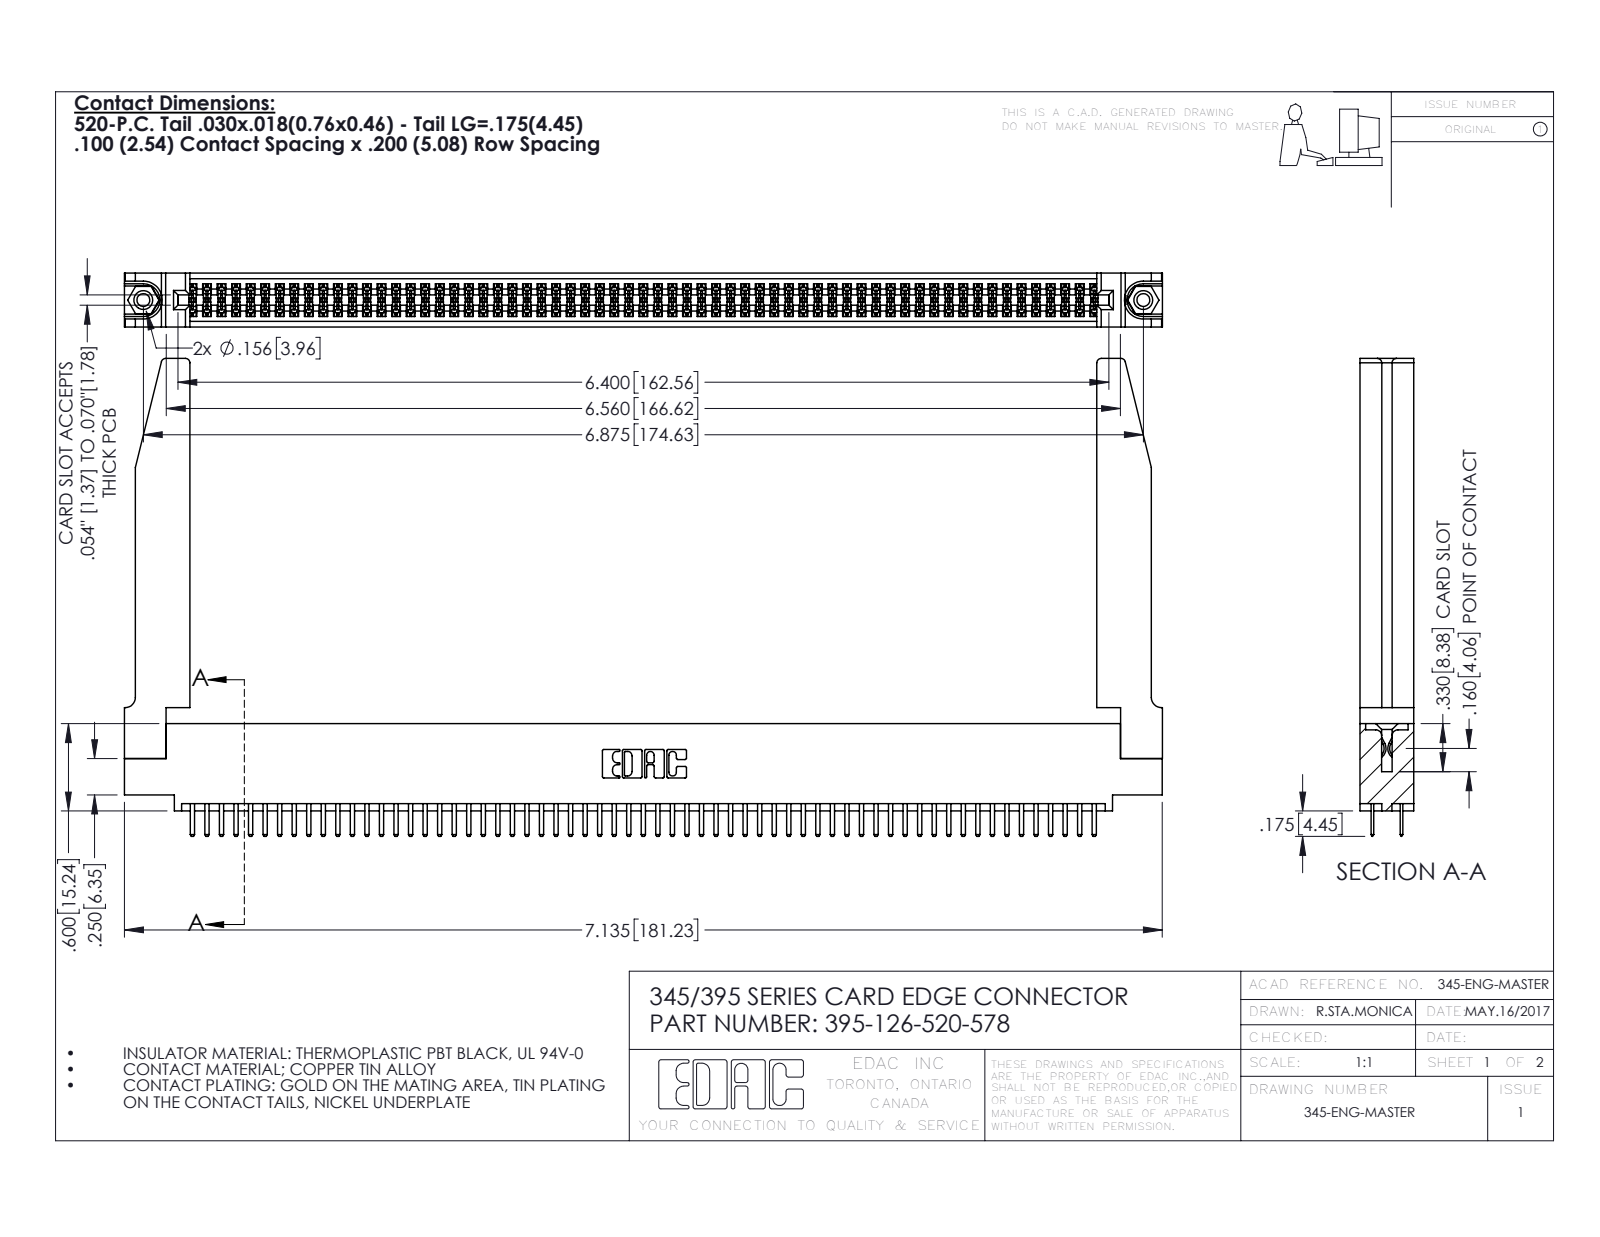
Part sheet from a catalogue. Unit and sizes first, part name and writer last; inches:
Units: inches
Overall size (bounding box): 7.136 × 3.285 × 0.37
Round holes (diameter × count): ⌀0.089 ×2, ⌀0.125 ×2, ⌀0.156 ×2, ⌀0.064 ×1
Round bosses / shafts (diameter × count): ⌀0.155 ×2
Partial cylindrical surfaces — rounded edges, fillets, slot ends (radius × count): R0.006 ×189, R0.01 ×130, R0.01 ×22, R0.03 ×8, R0.007 ×6, R0.031 ×6, R0.026 ×3, R0.014 ×2
Main face-to-face distances: 0.072, 0.37, 0.298, 0.2, 0.098, 0.272, 0.025, 0.225, 0.022, 0.072
Hole centre spacings: 0.27, 6.639, 6.875
Volume: 1.553 in³ · Surface area: 51.68 in²
Bodies: 131 solids, 7168 faces (4636 planar, 2480 cylindrical, 52 other)
Part name (STEP PRODUCT): 395-126-520-578; 345-220-078_345-220-078; 345-250-001_345-250-001-102; 345 Part_0.110 Offset - 0.156 Dia-TH (+1 more)
STEP written by: SolidWorks 2016 (CONFIG_CONTROL_DESIGN)
